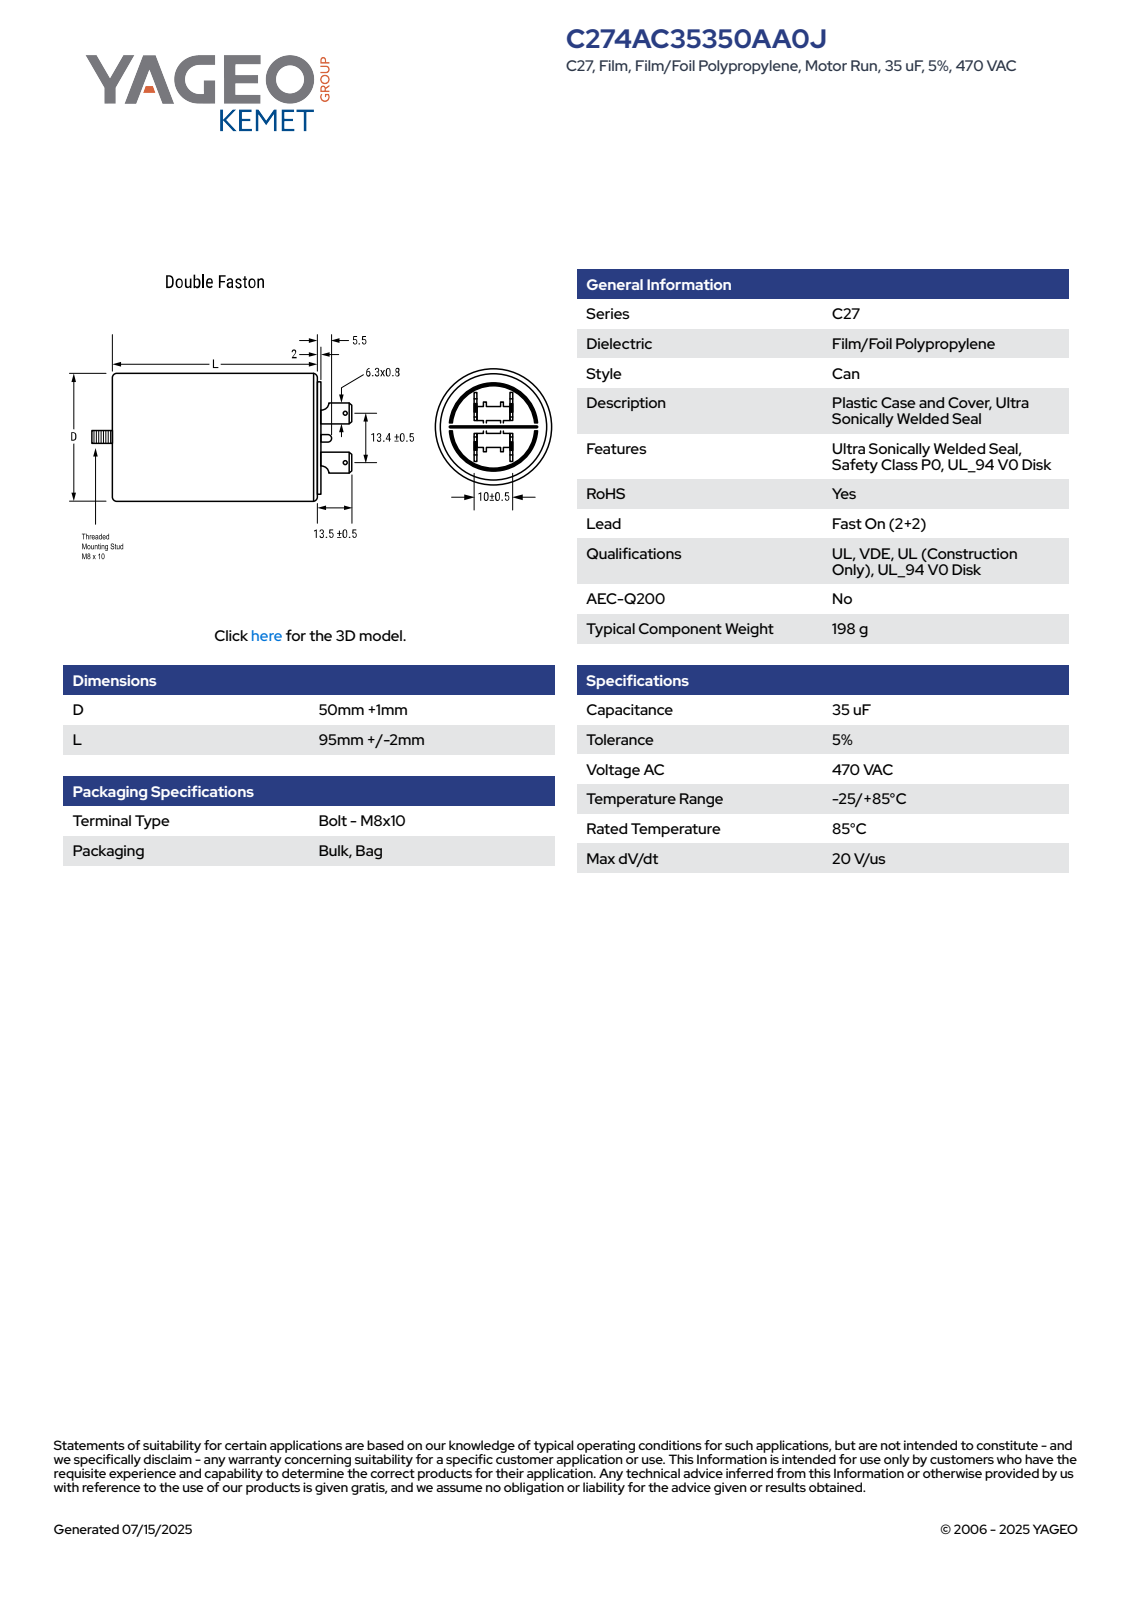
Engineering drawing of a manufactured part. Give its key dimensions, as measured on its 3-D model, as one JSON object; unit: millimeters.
{"part_name": "CFM_C27DF_50X95_D51L97", "step_written_by": "SolidWorks 2014 (AUTOMOTIVE_DESIGN)", "units": "millimeters", "bodies": {"solids": 1, "faces": 137, "planar": 49, "cylindrical": 53, "other": 35}, "overall_size": [121, 51, 51], "volume_mm3": 201094, "surface_area_mm2": 20773, "round_holes": [[1.2, 2]], "round_bosses_or_shafts": [[51, 1], [39.23, 1], [8, 1]], "partial_cylinders_radius": [[0.25, 9], [4, 2], [25.49, 1]], "face_to_face_distances": [99, 97, 2, 0.8, 9.7, 8.9, 10.5, 0.5, 10, 107], "hole_center_spacings": [13.9]}
